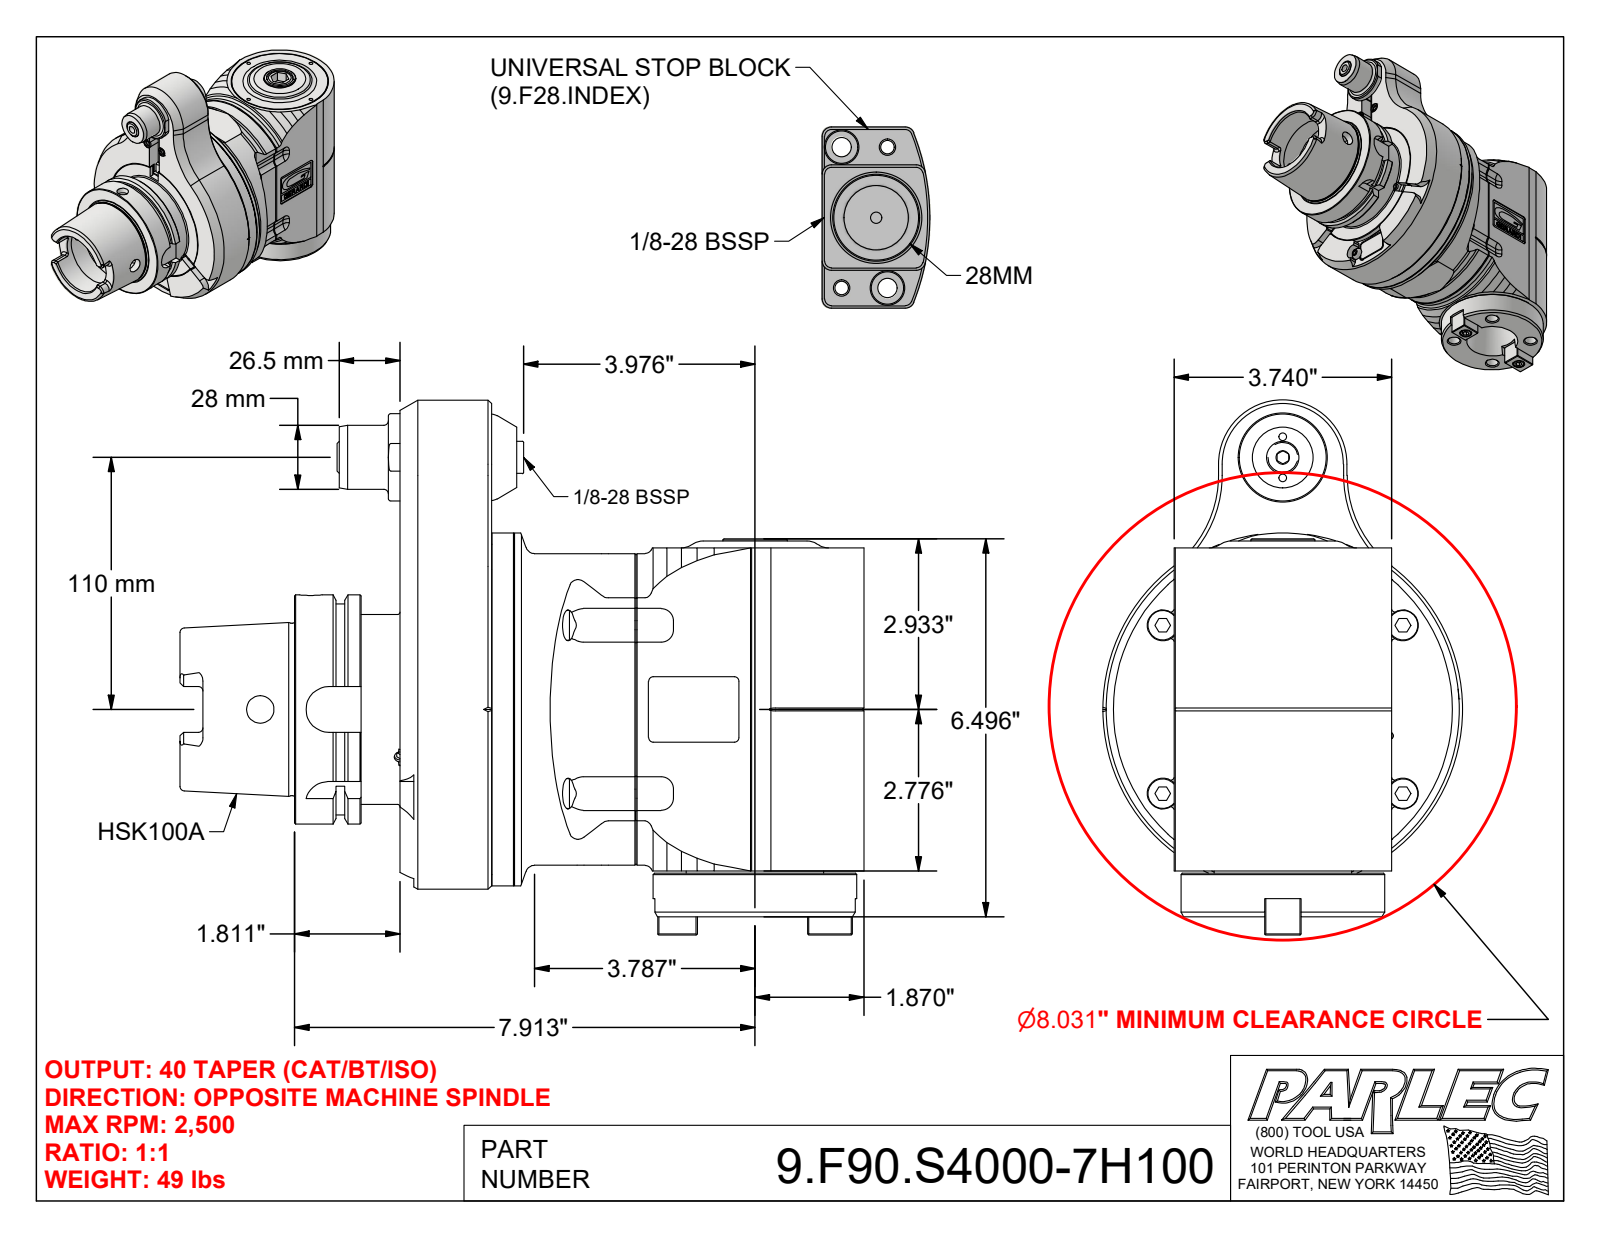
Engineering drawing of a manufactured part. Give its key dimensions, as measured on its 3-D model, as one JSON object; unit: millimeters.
{"part_name": "9.F90.S4000-7H100; 9_GA3_511_2 (Type 3, H100A, 110mm); 9FL3ATC; 9F28T300 (+2 more)", "step_written_by": "Autodesk Inventor 2022 (AUTOMOTIVE_DESIGN)", "units": "millimeters", "bodies": {"solids": 7, "faces": 937, "planar": 416, "cylindrical": 246, "other": 275}, "overall_size": [298.5, 233.5, 157], "volume_mm3": 3264000, "surface_area_mm2": 357900, "round_holes": [[10.5, 21], [3.2, 6], [6.8, 4], [8.5, 4], [10.3, 4], [13.5, 4], [5, 3], [4.2, 2], [5.3, 2], [6, 2], [8, 2], [12.5, 2]], "round_bosses_or_shafts": [[13, 4], [8, 4], [10, 3], [28, 2], [12, 2], [6.5, 2], [2.5, 2], [154, 1]], "partial_cylinders_radius": [[2, 18], [7, 12], [10, 8], [3, 6], [1, 4], [4, 4], [4.9, 4], [5, 4]], "face_to_face_distances": [5, 35, 30, 1, 29, 15.5, 6, 95, 19.5, 14.5], "hole_center_spacings": [64, 27.9, 66.4, 11.8, 57, 128, 25.3, 29.1]}
